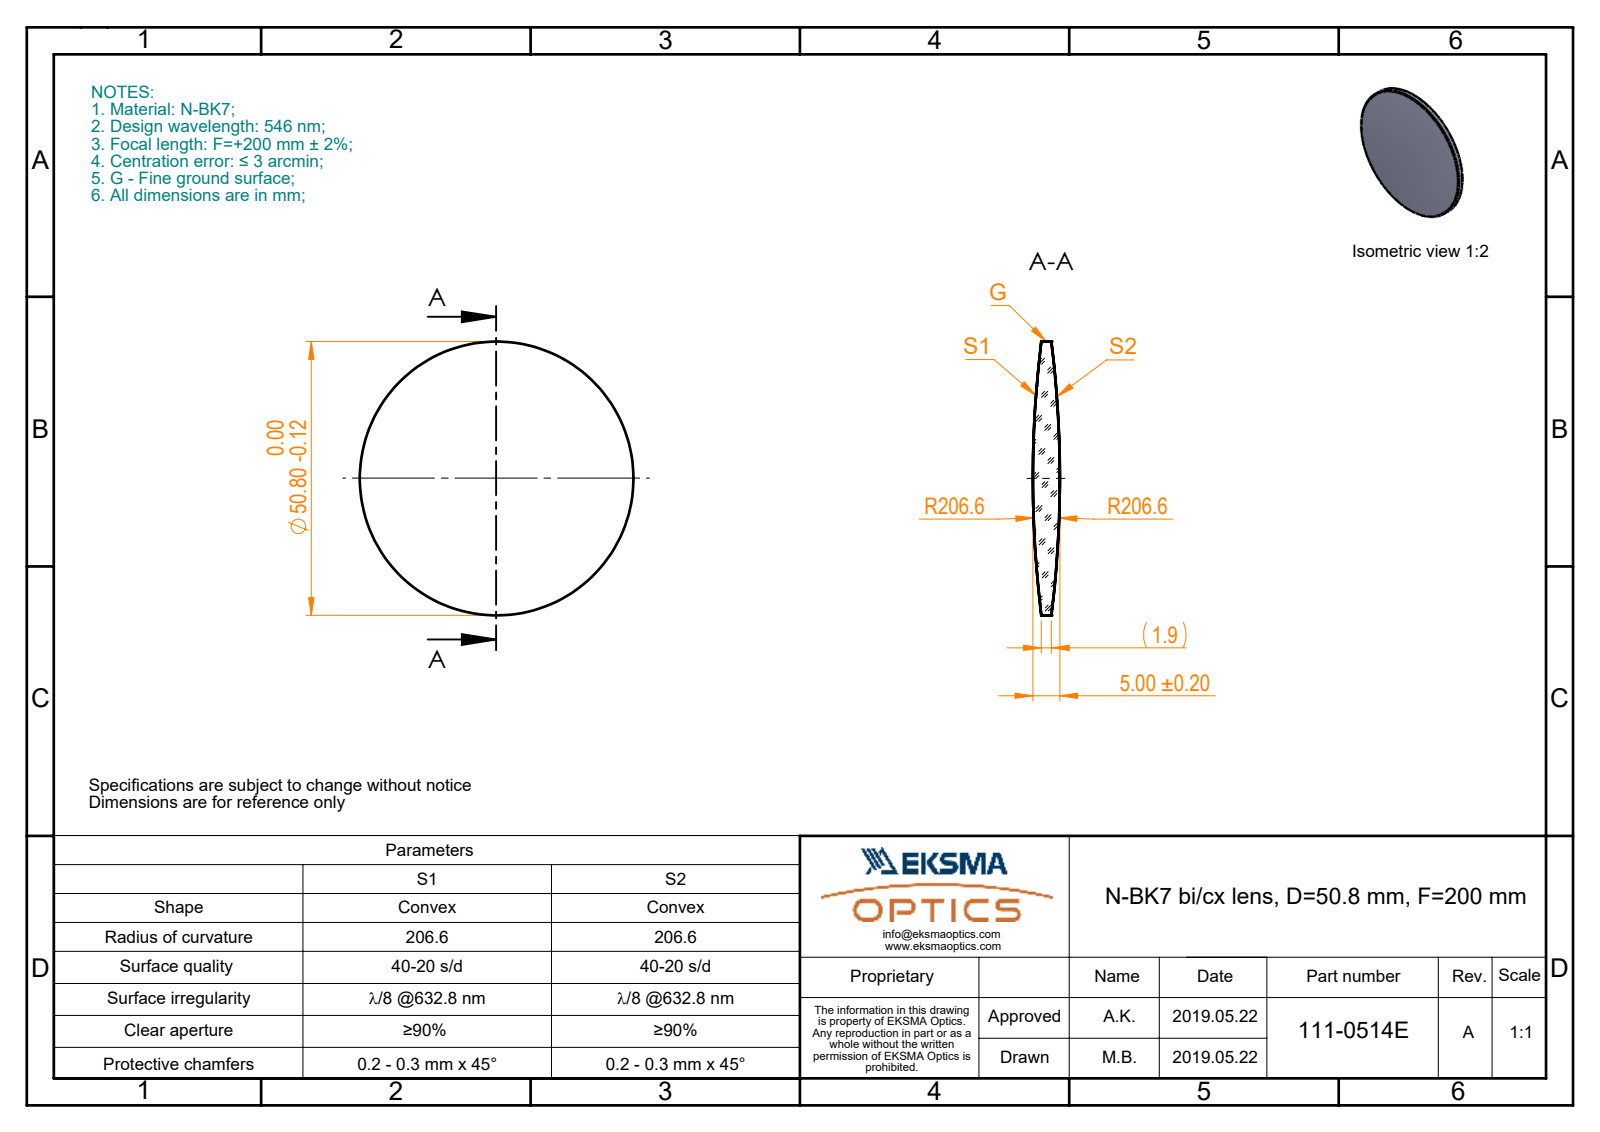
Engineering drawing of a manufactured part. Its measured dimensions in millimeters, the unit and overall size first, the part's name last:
Units: millimetres
Overall size (bounding box): 50.8 × 50.8 × 5
Round bosses / shafts (diameter × count): ⌀50.8 ×1
Volume: 6 961 mm³ · Surface area: 4 367 mm²
Bodies: 1 solid, 6 faces (0 planar, 2 cylindrical, 4 other)
Part name (STEP PRODUCT): 111-0514E BK7 bi-cx 50.8 F200
STEP written by: SolidWorks 2017 (CONFIG_CONTROL_DESIGN)
